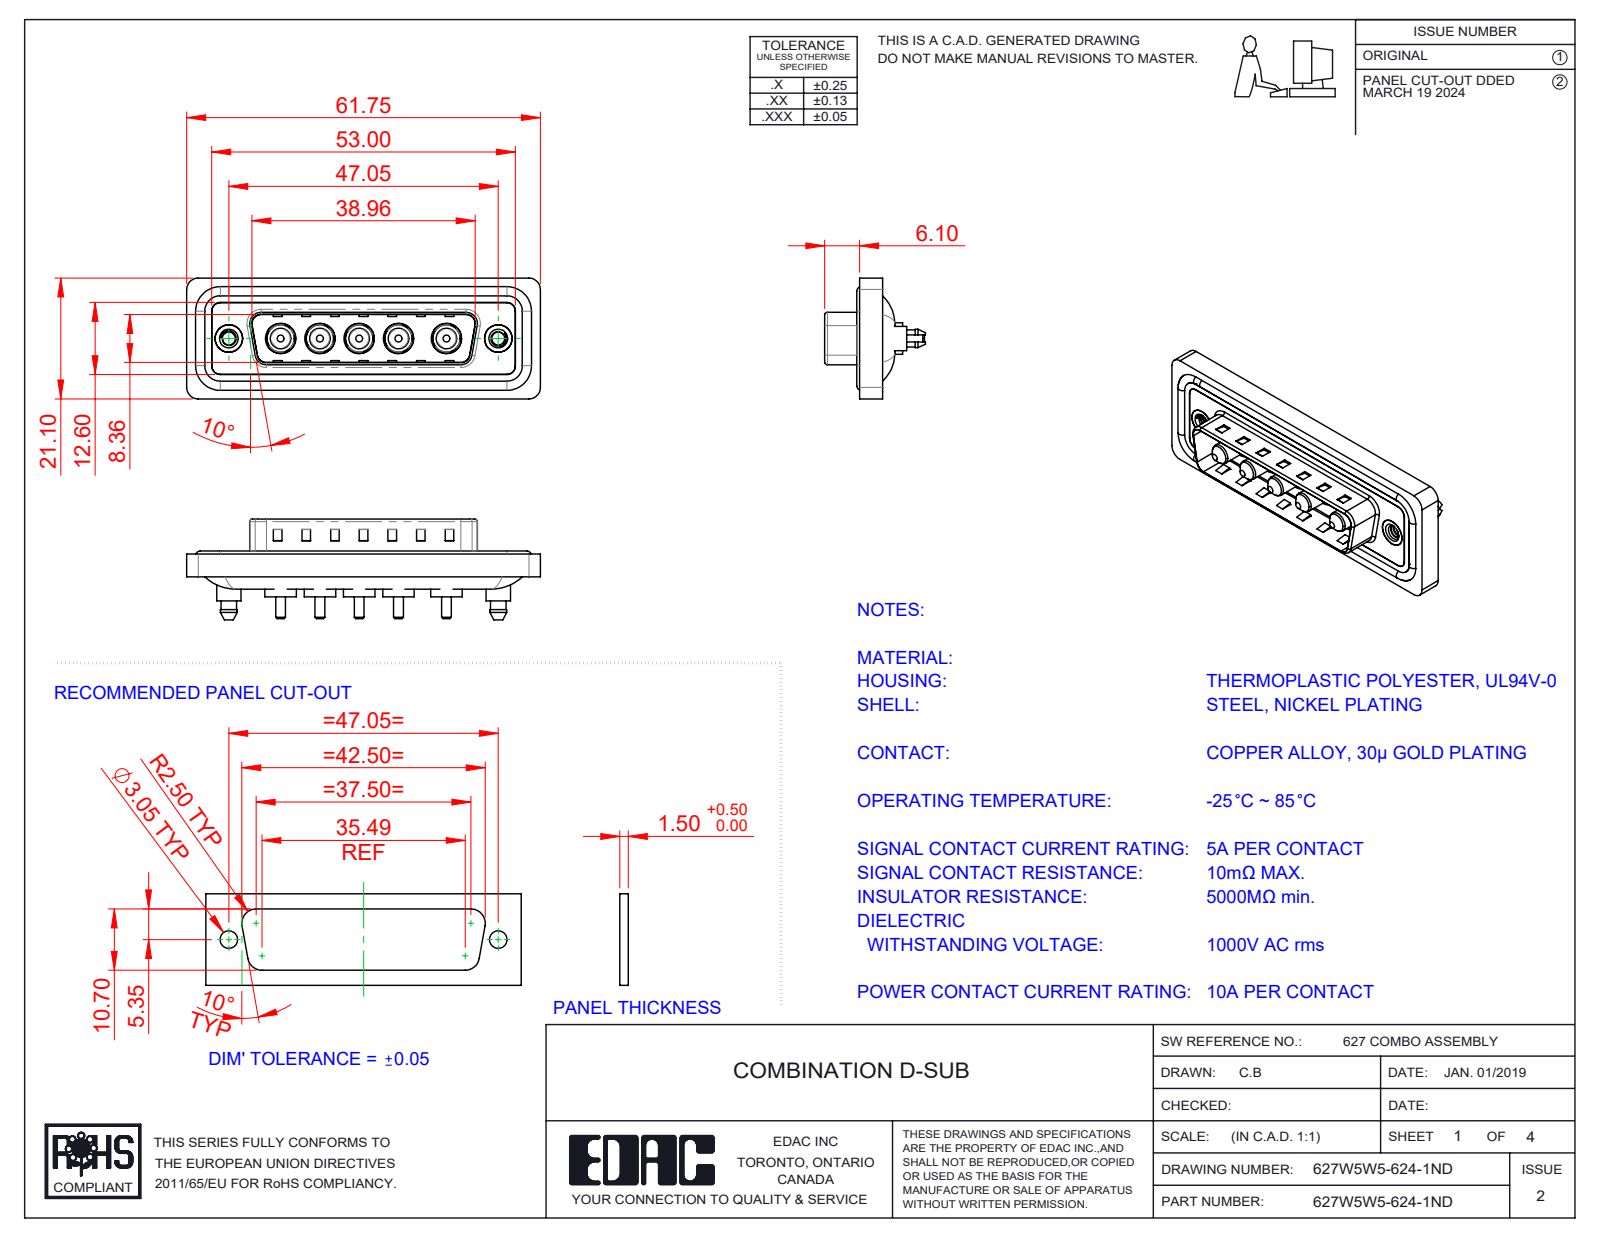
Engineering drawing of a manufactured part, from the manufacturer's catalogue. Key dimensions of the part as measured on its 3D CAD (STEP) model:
Part name (STEP PRODUCT): Power Pin_10A S; 627Combo Shell Rear_25 Contacts; 627Combo Shell Front_25 Contacts; 627Combo Threaded Boardlock_5 (+4 more)
STEP written by: SolidWorks 2023 (CONFIG_CONTROL_DESIGN)
Units: millimetres
Bodies: 17 solids, 736 faces (275 planar, 323 cylindrical, 138 other)
Overall size (bounding box): 61.75 × 21.1 × 17.6
Volume: 7 534 mm³ · Surface area: 12 069 mm²
Round holes (diameter × count): ⌀4.85 ×5, ⌀5.3 ×5, ⌀2.26 ×2, ⌀4 ×2, ⌀4.8 ×2, ⌀5 ×2
Round bosses / shafts (diameter × count): ⌀5.5 ×5, ⌀5.2 ×5, ⌀4.75 ×5, ⌀3.75 ×5, ⌀3.6 ×5, ⌀1.7 ×5, ⌀1.6 ×4, ⌀5.4 ×2
Partial cylindrical surfaces — rounded edges, fillets, slot ends (radius × count): R1.5 ×24, R2 ×18, R1.6 ×10, R0.5 ×8, R2.1 ×5, R0.25 ×4, R0.6 ×4, R0.65 ×4
Main face-to-face distances: 0.4, 1.5, 1.1, 0.5, 3.1, 1.6, 2.9, 0.82, 9.58, 5.65
Hole centre spacings: 6.86, 9.04, 13.73, 38.01, 6.87, 8.37, 8.38, 9.05
